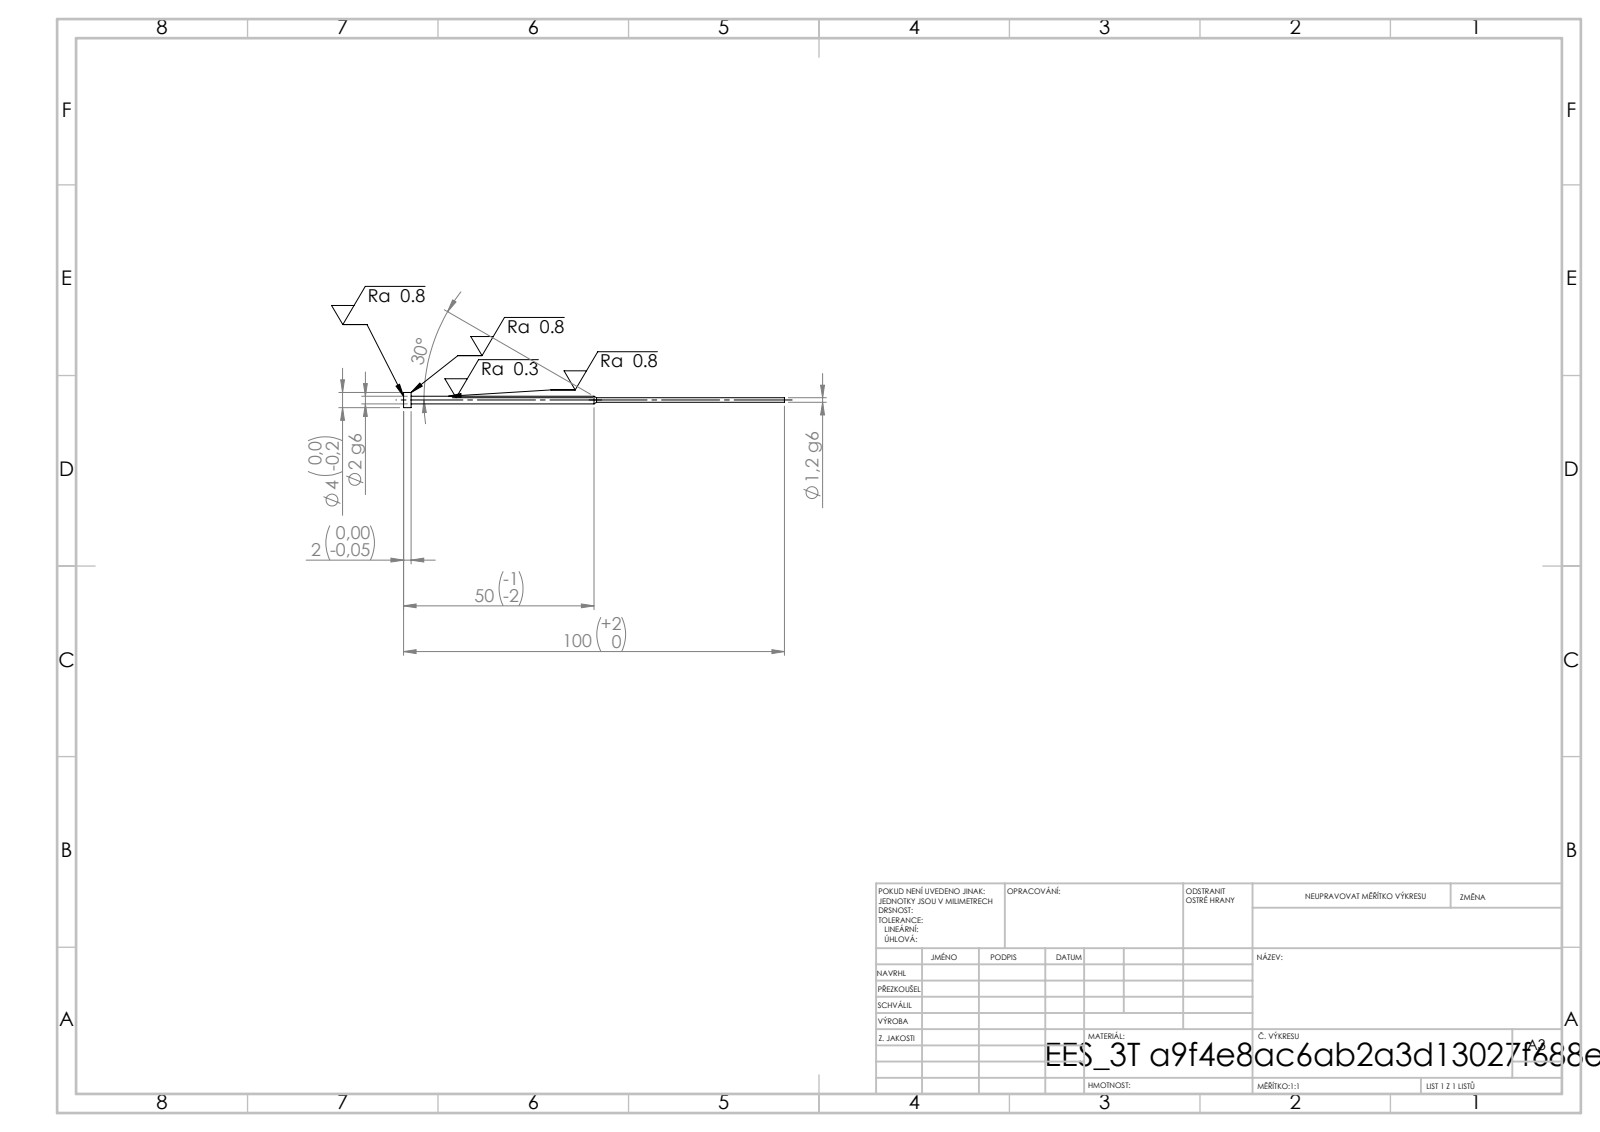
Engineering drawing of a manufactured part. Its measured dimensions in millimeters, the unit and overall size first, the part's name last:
Units: millimetres
Overall size (bounding box): 100 × 4 × 4
Round bosses / shafts (diameter × count): ⌀4 ×1, ⌀2 ×1, ⌀1.2 ×1
Main face-to-face distances: 2, 98, 100
Volume: 233 mm³ · Surface area: 540 mm²
Bodies: 1 solid, 11 faces (3 planar, 6 cylindrical, 2 other)
STEP written by: SolidWorks 2019 (CONFIG_CONTROL_DESIGN)
